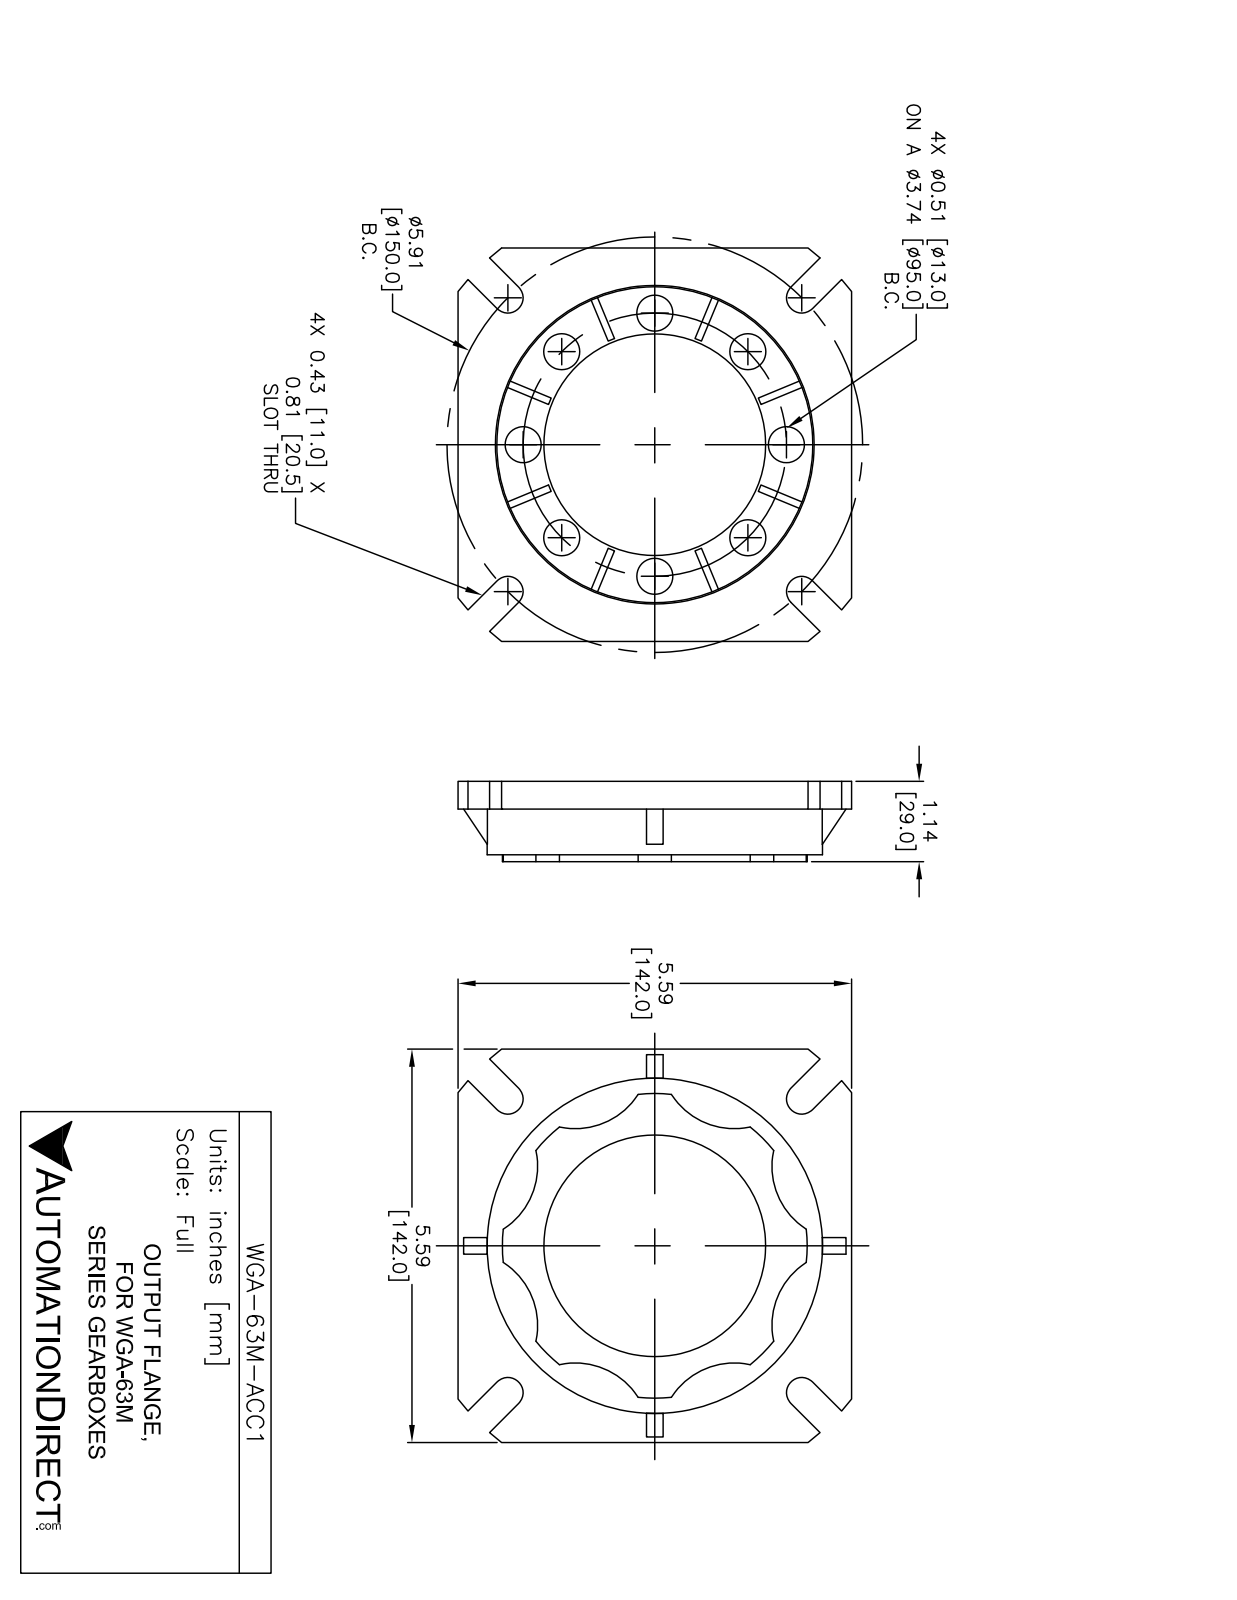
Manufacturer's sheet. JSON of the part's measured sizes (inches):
{"part_name": "WGA-63M-ACC1", "step_written_by": "SolidWorks 2014 (AUTOMOTIVE_DESIGN)", "units": "inches", "bodies": {"solids": 1, "faces": 119, "planar": 62, "cylindrical": 57, "other": 0}, "overall_size": [5.591, 5.591, 1.142], "volume_in3": 8.884, "surface_area_in2": 87, "round_holes": [[3.15, 1], [4.488, 1], [4.528, 1]], "round_bosses_or_shafts": [[0.512, 8], [4.764, 1]], "partial_cylinders_radius": [[1.063, 8], [0.217, 4], [2.165, 1], [3.543, 1]], "face_to_face_distances": [0.394, 0.098, 0.906, 0.512, 0.236, 0.748, 1.142, 0.138, 0.65, 1.043]}
